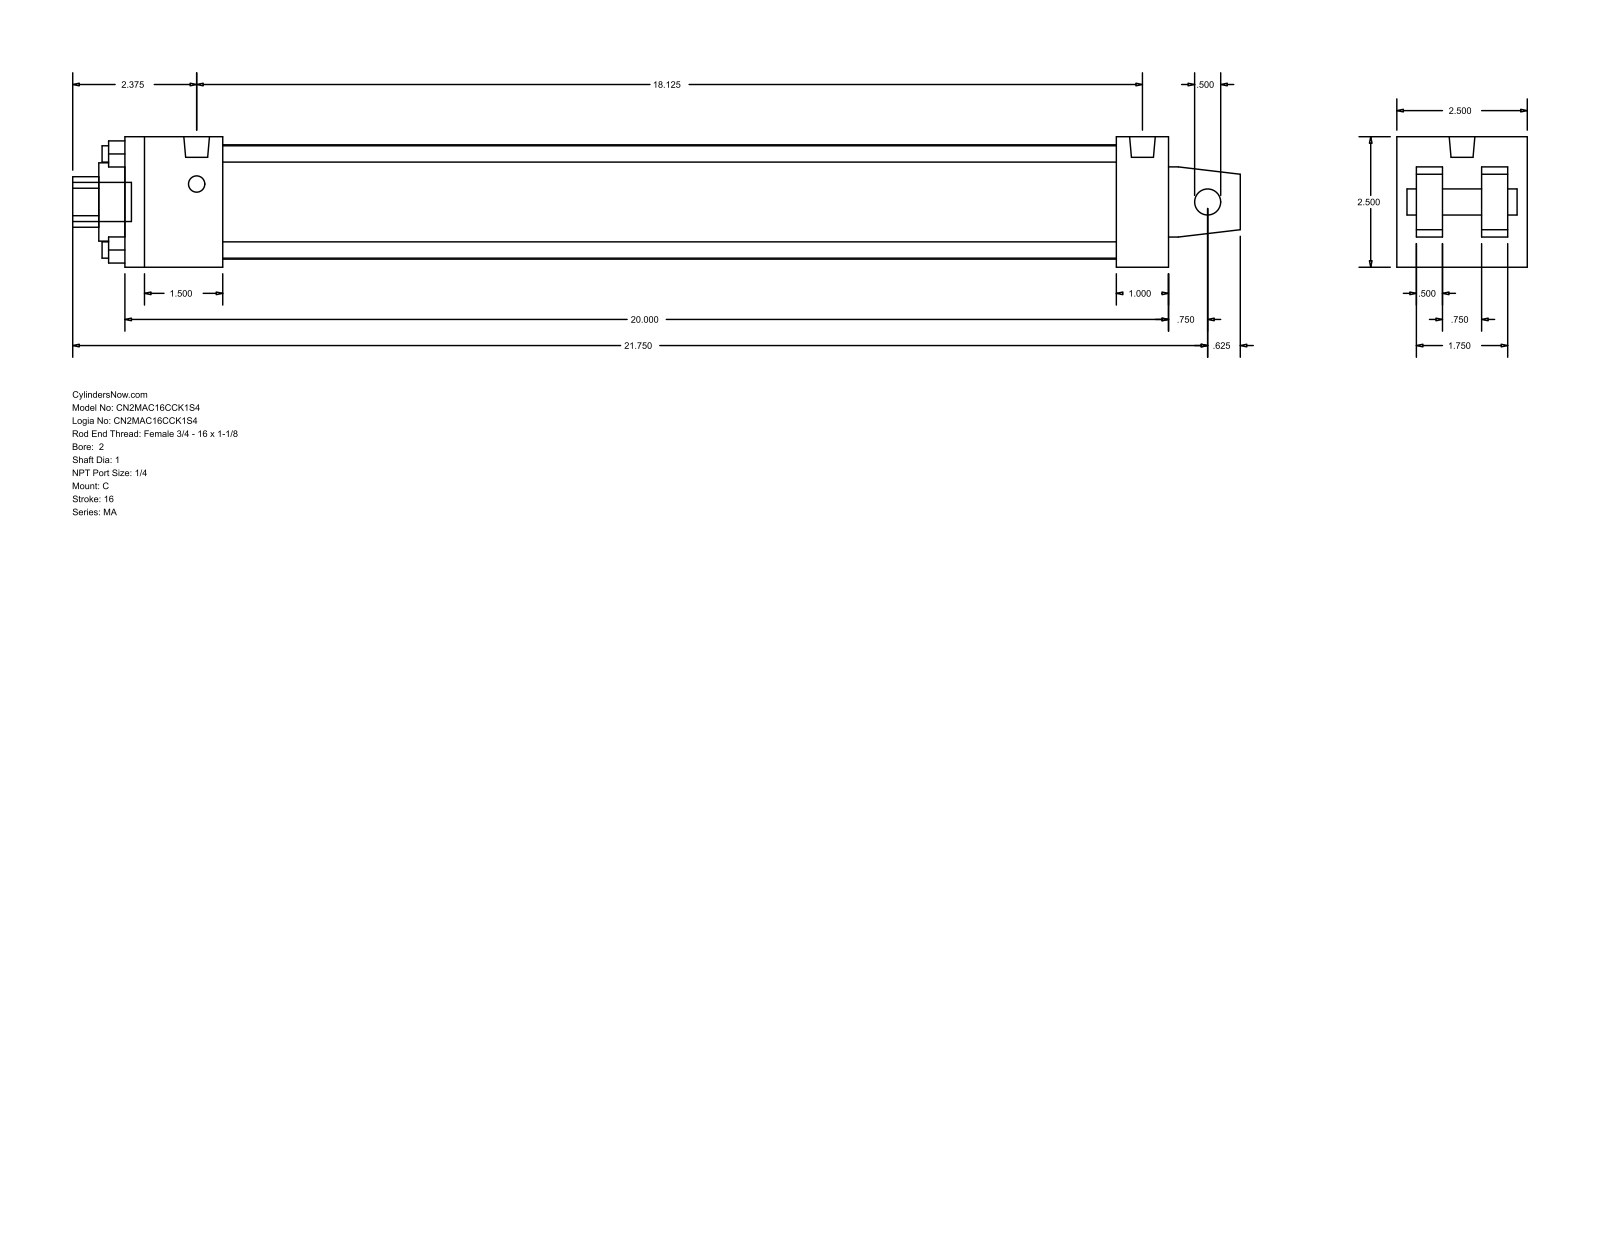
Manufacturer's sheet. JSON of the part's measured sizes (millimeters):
{"part_name": "MA_C__0200_1", "step_written_by": "GSSL Pune (CONFIG_CONTROL_DESIGN)", "units": "millimeters", "bodies": {"solids": 0, "faces": 103, "planar": 76, "cylindrical": 27, "other": 0}, "overall_size": [568.33, 63.5, 63.5], "round_holes": [[7.94, 4], [12.7, 1], [25.4, 1], [38.1, 1], [55.63, 1]], "round_bosses_or_shafts": [[7.94, 4], [12.49, 2], [19.05, 1]], "partial_cylinders_radius": [[12.29, 1]], "face_to_face_distances": [63.5, 12.7, 508, 22.22, 41.28, 9.52, 53.98, 31.76, 47.63, 25.4], "hole_center_spacings": [33.05, 46.74, 66.1]}
